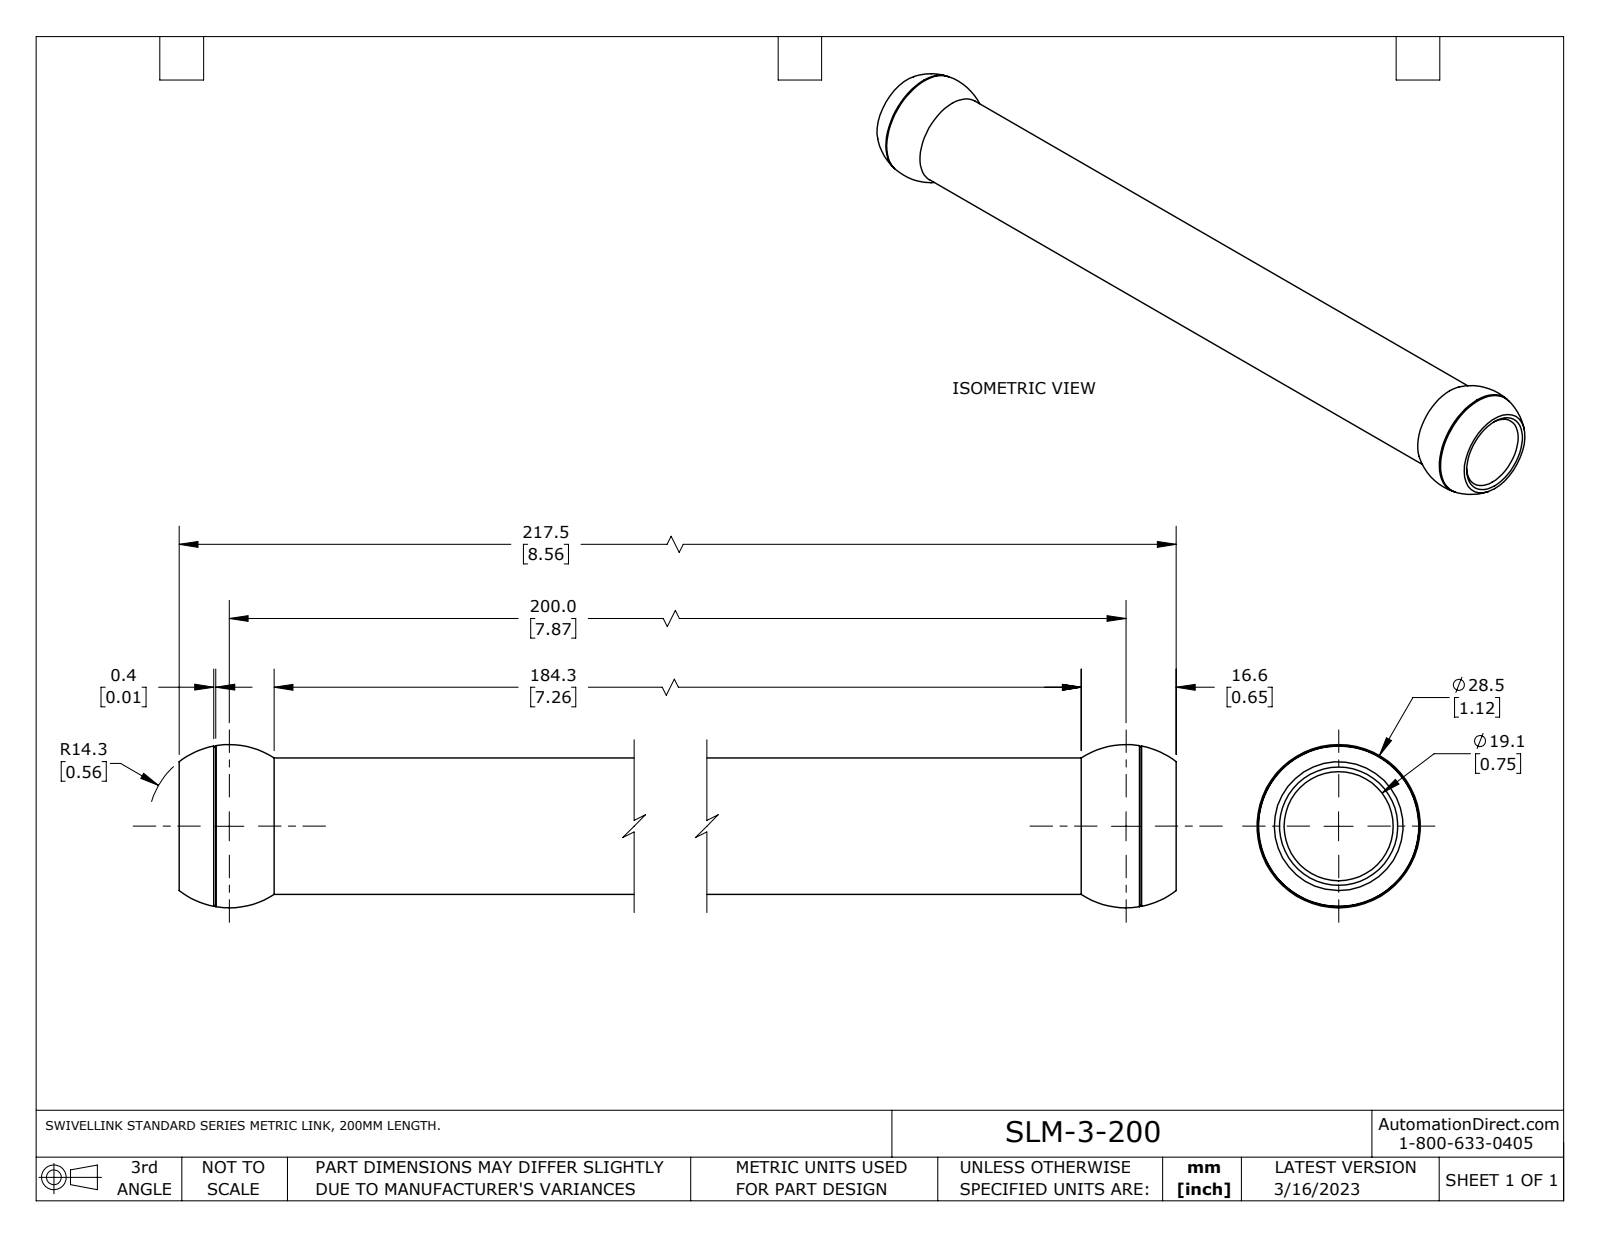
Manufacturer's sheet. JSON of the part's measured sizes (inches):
{"part_name": "SLM-3-200", "step_written_by": "SolidWorks 2021 (AUTOMOTIVE_DESIGN)", "units": "inches", "bodies": {"solids": 2, "faces": 14, "planar": 2, "cylindrical": 2, "other": 10}, "overall_size": [8.996, 1.107, 1.107], "volume_in3": 8.748, "surface_area_in2": 48.73, "round_bosses_or_shafts": [[0.937, 1], [0.75, 1]], "face_to_face_distances": [8.563]}
